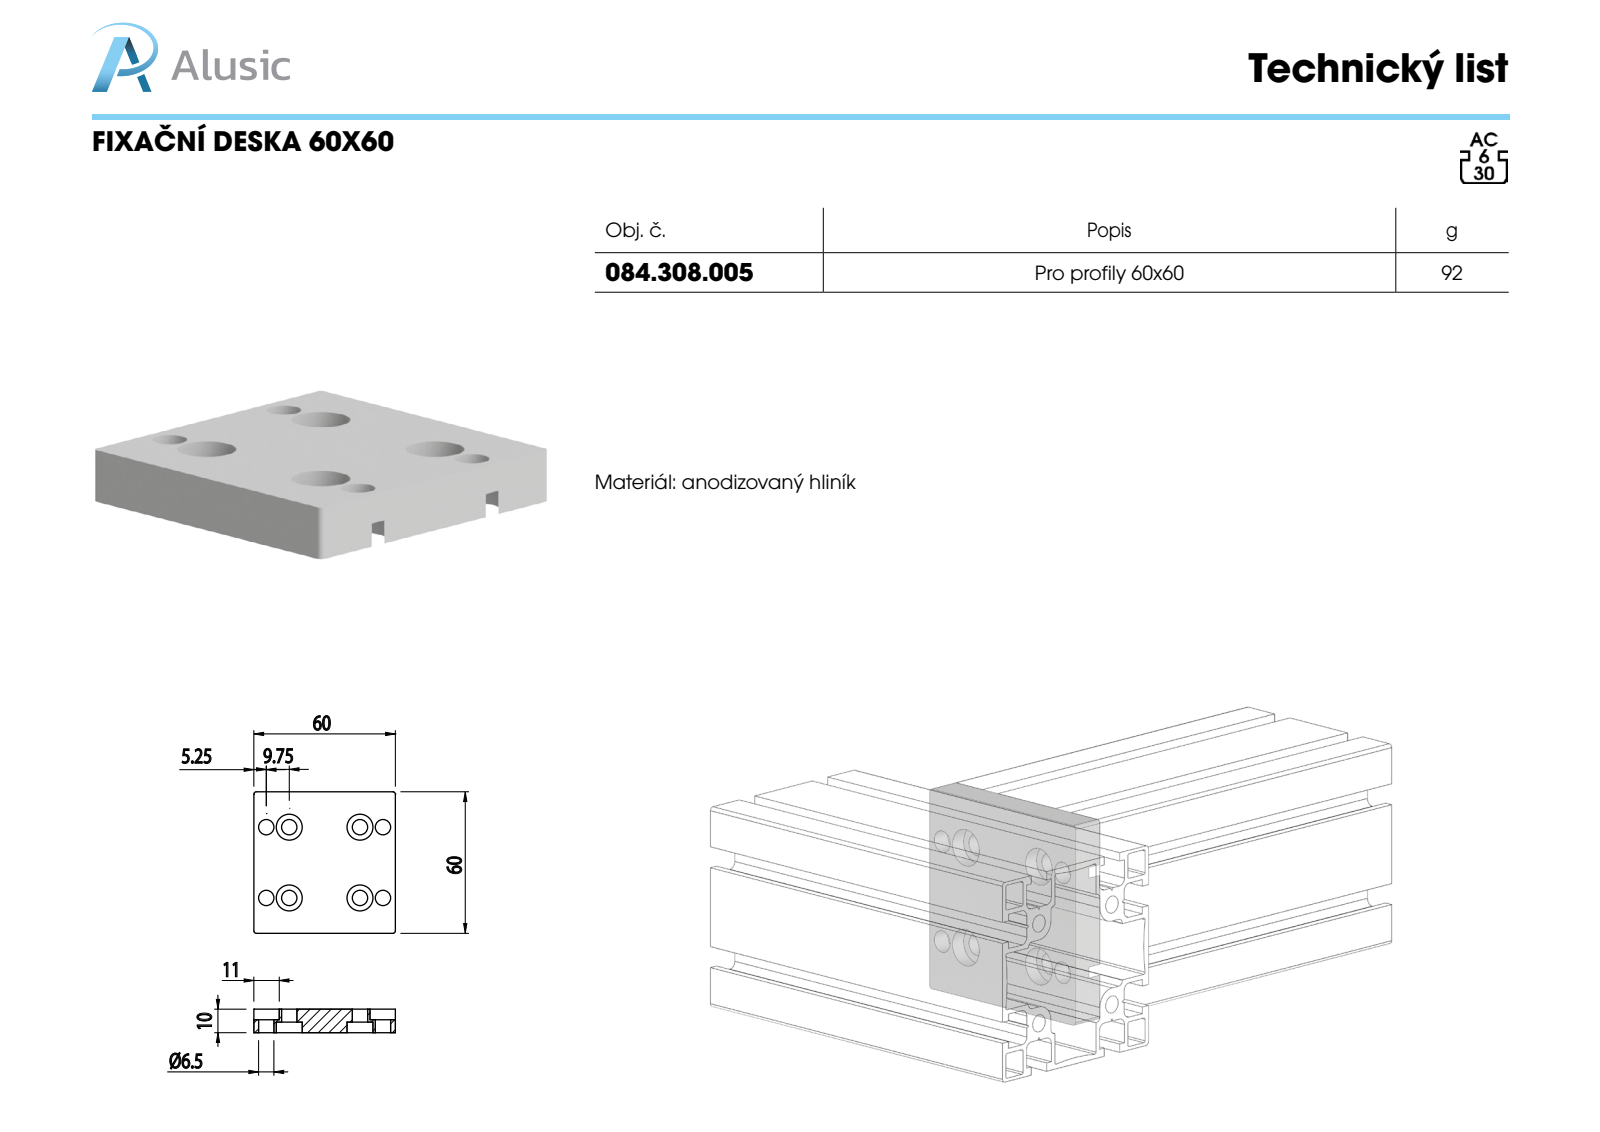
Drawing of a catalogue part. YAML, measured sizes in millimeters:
part_name: "084.308.005"
step_written_by: "SolidWorks 2011 (CONFIG_CONTROL_DESIGN)"
units: millimeters
bodies: {solids: 1, faces: 48, planar: 14, cylindrical: 34, other: 0}
overall_size: [60, 60, 10]
volume: 31120
surface_area: 11074
round_holes:
  - {diameter: 6.5, count: 8}
  - {diameter: 11, count: 8}
partial_cylinders:
  - {radius: 1, count: 4}
face_to_face_distances: [10, 60, 4.5, 5.5, 1]
hole_center_spacings: [30, 9.75, 31.54, 39.75, 49.8, 42.43, 49.5, 57.88]
